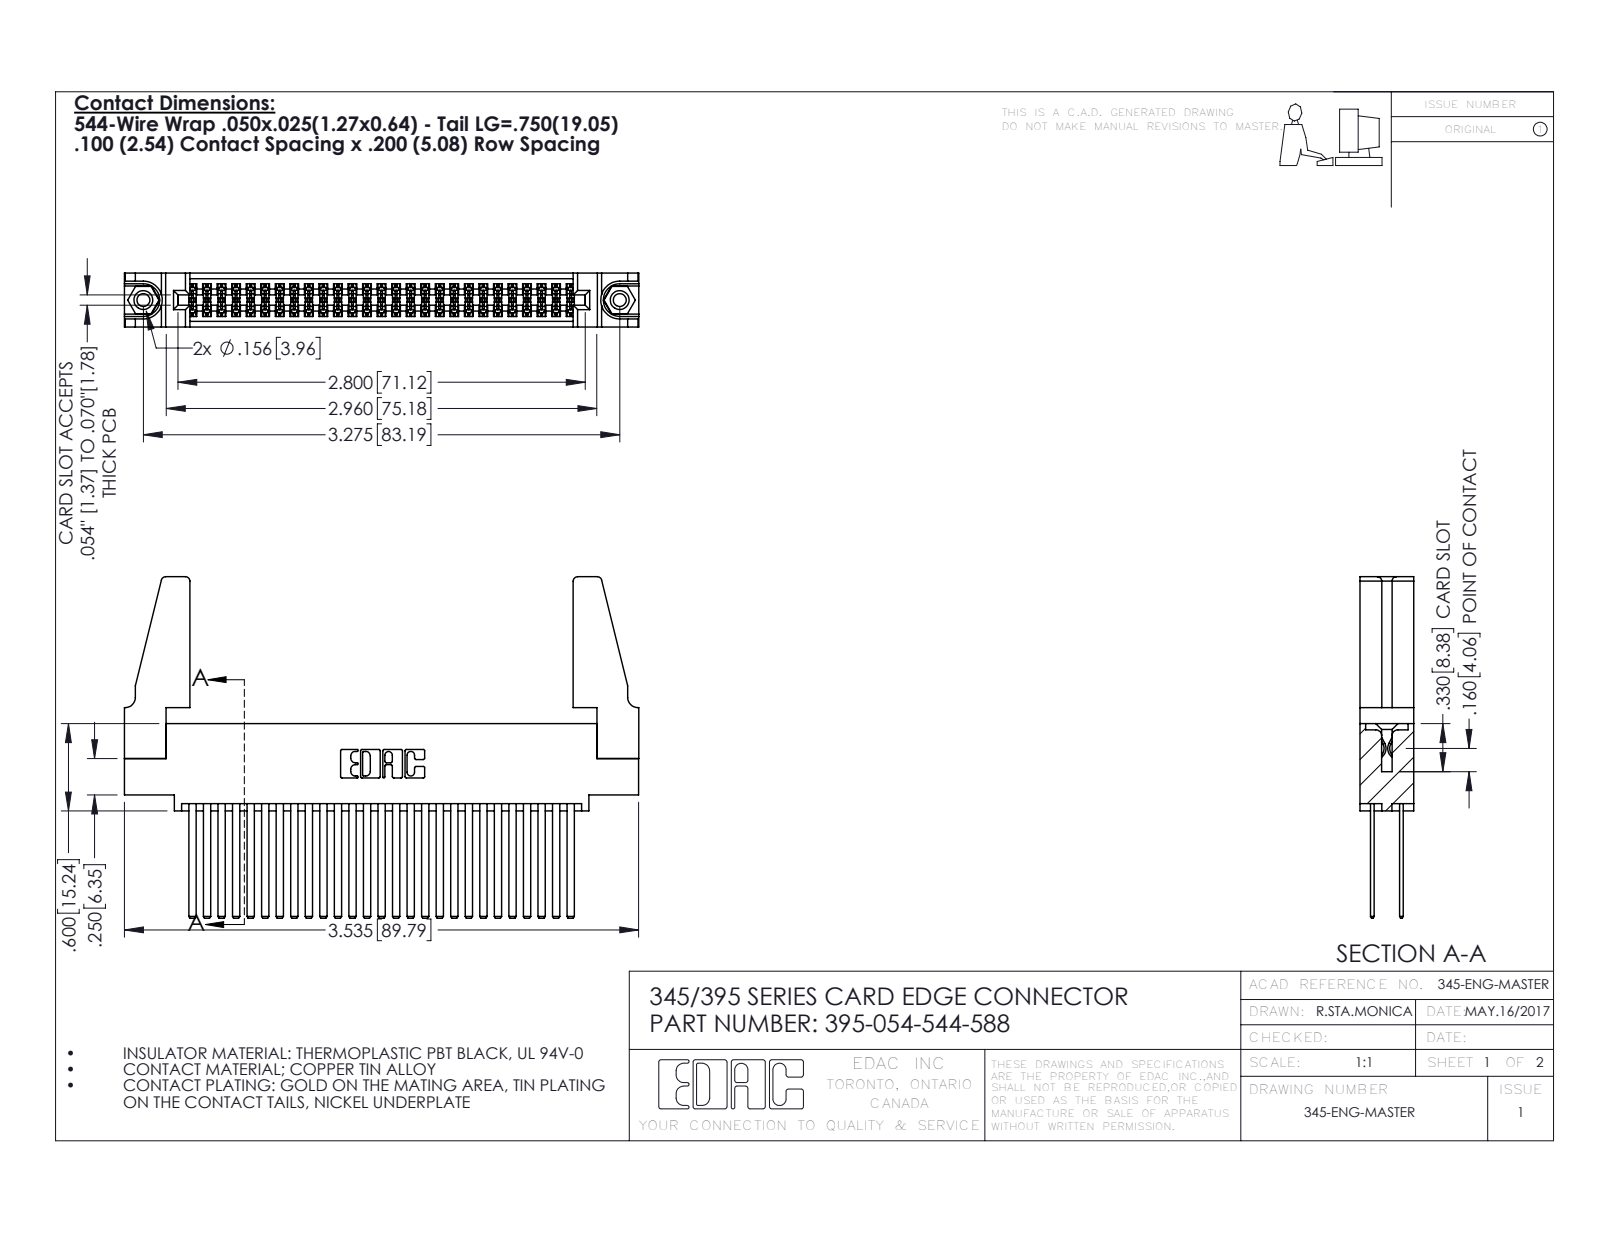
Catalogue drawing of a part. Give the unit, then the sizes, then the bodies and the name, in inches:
Units: inches
Overall size (bounding box): 3.536 × 2.347 × 0.37
Round holes (diameter × count): ⌀0.089 ×2, ⌀0.125 ×2, ⌀0.156 ×2, ⌀0.064 ×1
Round bosses / shafts (diameter × count): ⌀0.155 ×2
Partial cylindrical surfaces — rounded edges, fillets, slot ends (radius × count): R0.006 ×81, R0.01 ×22, R0.03 ×8, R0.007 ×6, R0.031 ×6, R0.026 ×3, R0.014 ×2, R0.019 ×2
Main face-to-face distances: 0.072, 0.298, 0.2, 0.098, 0.272, 0.025, 0.37, 0.225, 0.175, 0.149
Hole centre spacings: 0.27, 3.04, 3.275
Volume: 0.764 in³ · Surface area: 29.21 in²
Bodies: 59 solids, 2630 faces (1722 planar, 892 cylindrical, 16 other)
Part name (STEP PRODUCT): 345 Part_0.110 Offset - 0.156 Dia-TH; 395-054-544-588; 345-220-078_345-220-088; 345-250-001_345-250-001-102 (+1 more)
STEP written by: SolidWorks 2016 (CONFIG_CONTROL_DESIGN)
